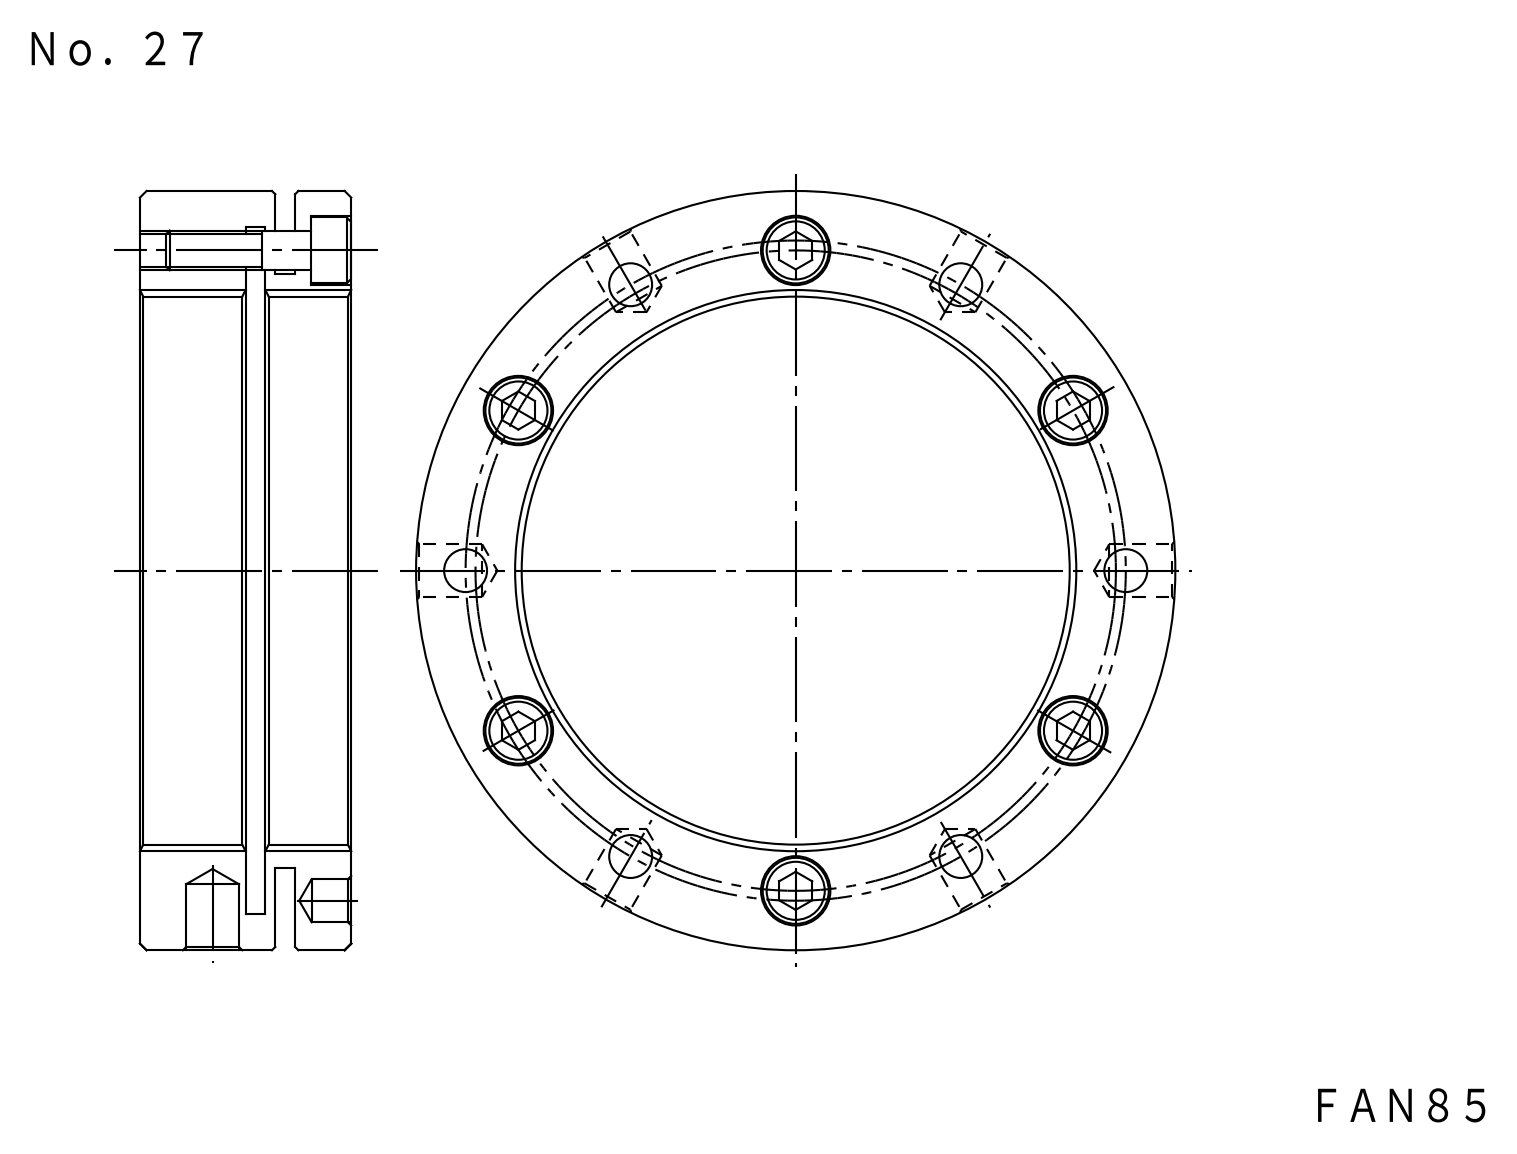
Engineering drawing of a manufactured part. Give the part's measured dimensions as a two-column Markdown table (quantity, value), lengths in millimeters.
| quantity | value |
| --- | --- |
| part name | FKD FAN85; M6X22_default |
| STEP written by | SolidWorks 2012 (CONFIG_CONTROL_DESIGN) |
| units | millimeters |
| bodies | 7 solids, 204 faces (72 planar, 108 cylindrical, 24 other) |
| overall size | 115 × 115 × 32 |
| volume | 129 960 mm³ |
| surface area | 52 454 mm² |
| round holes (diameter × count) | 6.3 × 6, 6.5 × 6, 10.5 × 6, 4.92 × 3, 4.92 × 3, 8 × 3, 85 × 1, 108 × 1 |
| round bosses / shafts (diameter × count) | 10 × 6, 6 × 6, 115 × 1, 94 × 1 |
| main face-to-face distances | 2.5, 4, 32, 17, 15, 19.5, 12.5, 21, 1.5, 11 |
| hole center spacings | 50, 50.5, 97.07, 26.02, 71.06, 86.6, 26.01, 71.07 |
